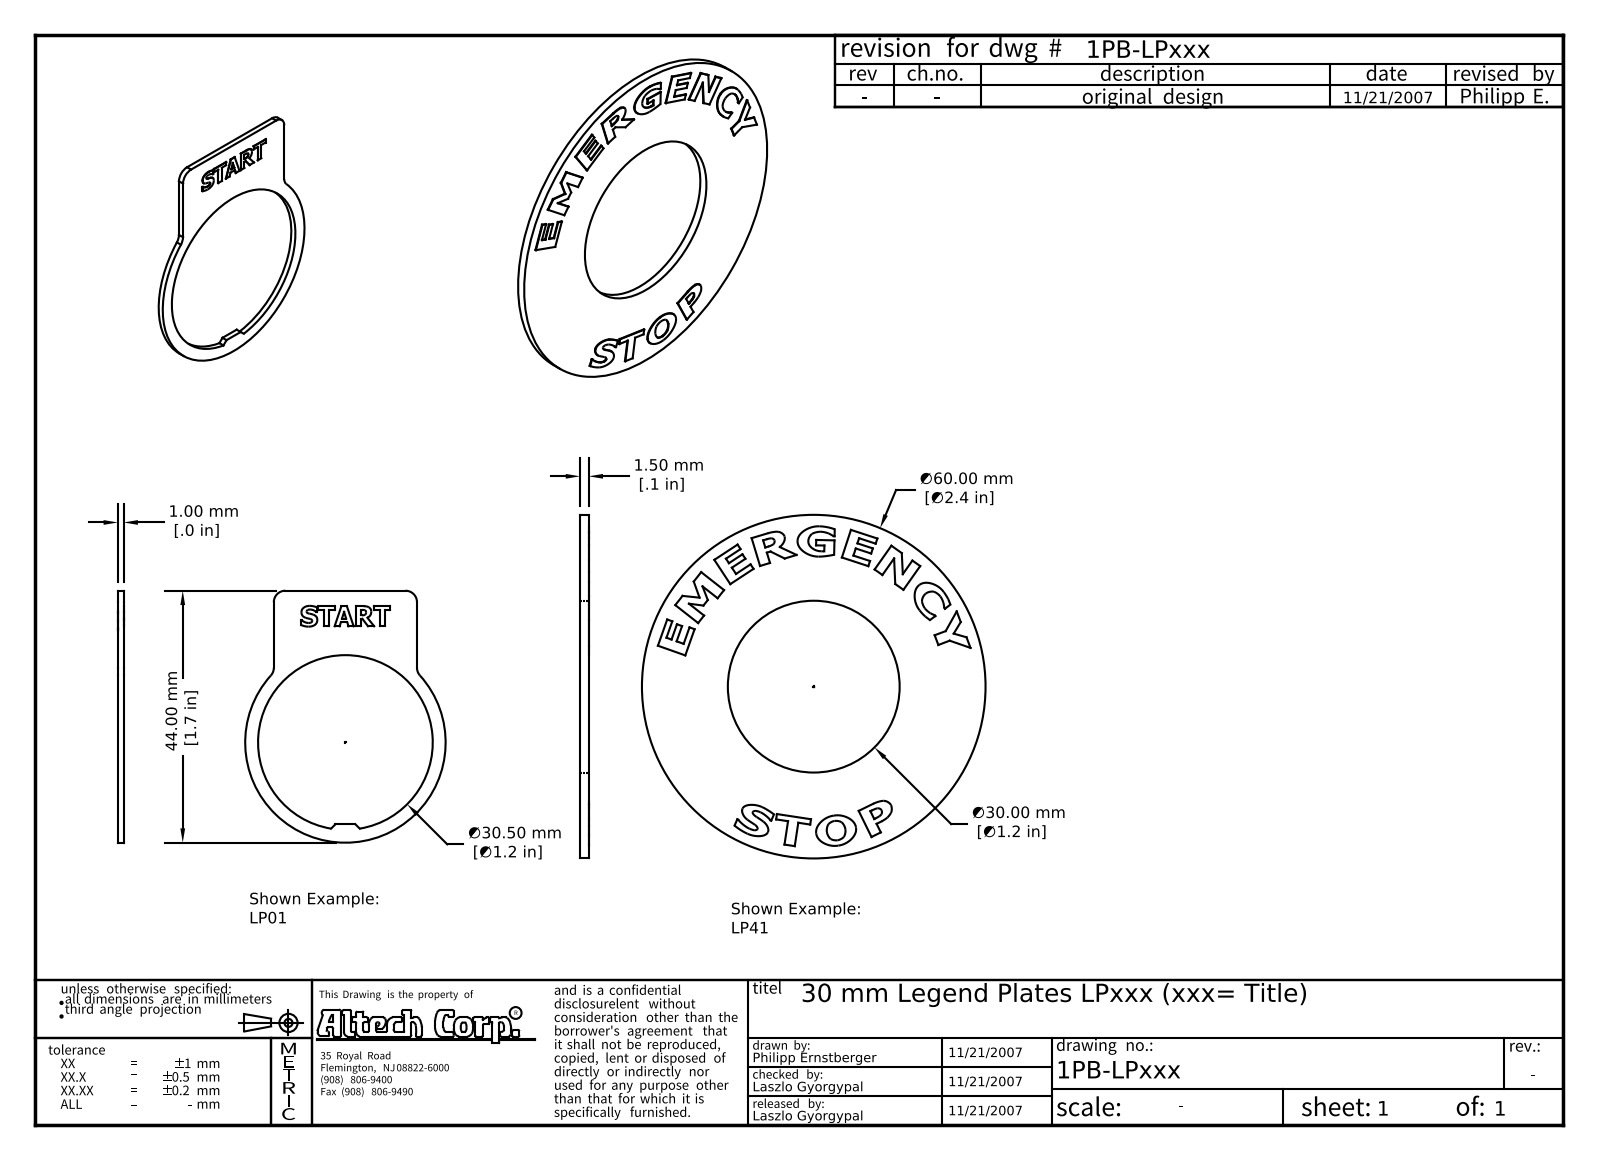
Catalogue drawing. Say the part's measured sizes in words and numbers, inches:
The part is named "LP01". Its 3-D file was written by "Autodesk Inventor 2008 (AUTOMOTIVE_DESIGN)". It is 1 solid with 158 faces: 106 planar, 6 cylindrical and 46 other. Overall it measures 1.732 by 1.378 by 0.04 inches. Its volume is 0.031 cubic inches and its surface area 1.908 square inches. Round holes: 1 of diameter 1.201. Partial cylindrical surfaces (rounded edges, fillets, slot ends): 4 of radius 0.079, 1 of radius 0.689. The main face-to-face distances are 0.039, 0.04, 0.04, 0.984, 1.606, 0.035, 0.138, 0.223, 0.026, 0.106.
